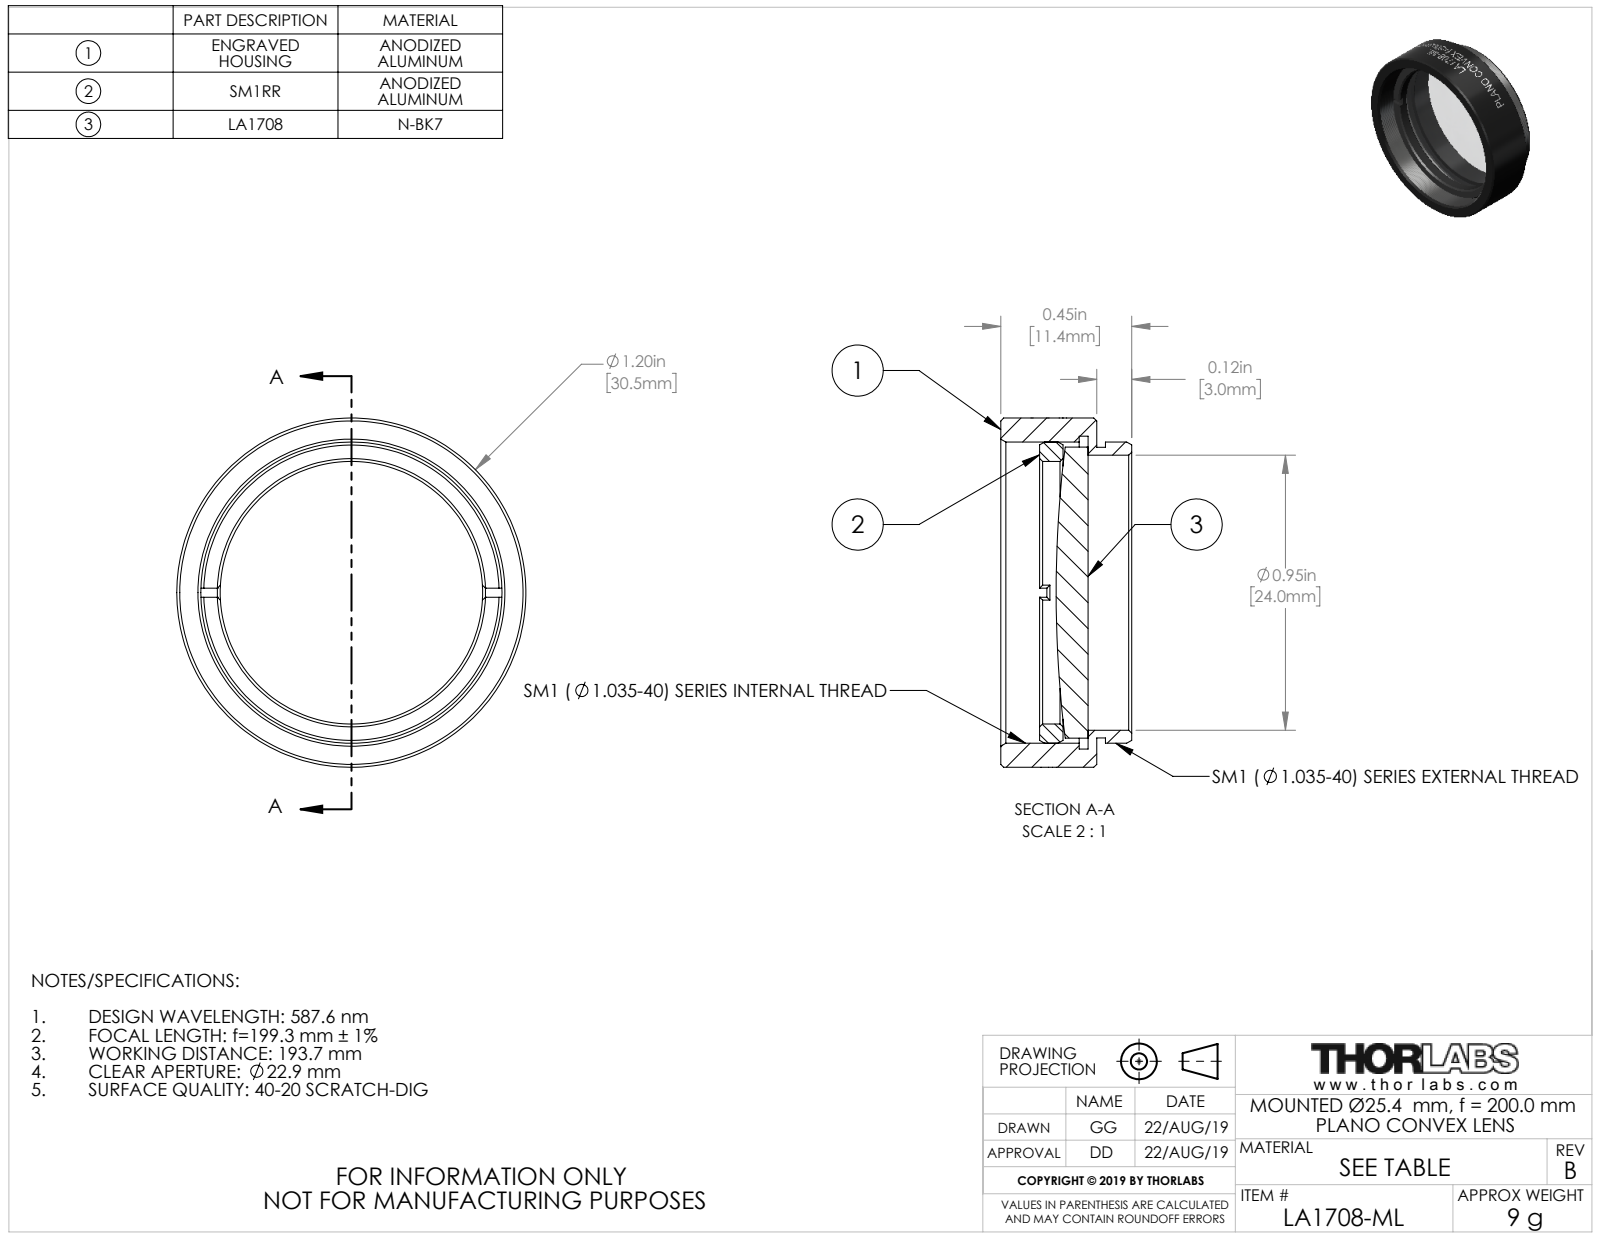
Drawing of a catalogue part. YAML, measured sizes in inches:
part_name: "24438-E0W"
step_written_by: "SolidWorks 2018 (CONFIG_CONTROL_DESIGN)"
units: inches
bodies: {solids: 3, faces: 120, planar: 20, cylindrical: 76, other: 24}
overall_size: [1.2, 1.2, 0.45]
volume: 0.201
surface_area: 6.687
round_holes:
  - {diameter: 0.902, count: 1}
  - {diameter: 0.945, count: 1}
  - {diameter: 1.075, count: 1}
round_bosses_or_shafts:
  - {diameter: 1.2, count: 1}
  - {diameter: 1.035, count: 1}
  - {diameter: 1, count: 1}
  - {diameter: 0.999, count: 1}
face_to_face_distances: [0.03, 0.33, 0.3, 0.116, 0.086, 0.214, 0.196, 0.166, 0.08, 0.134]
